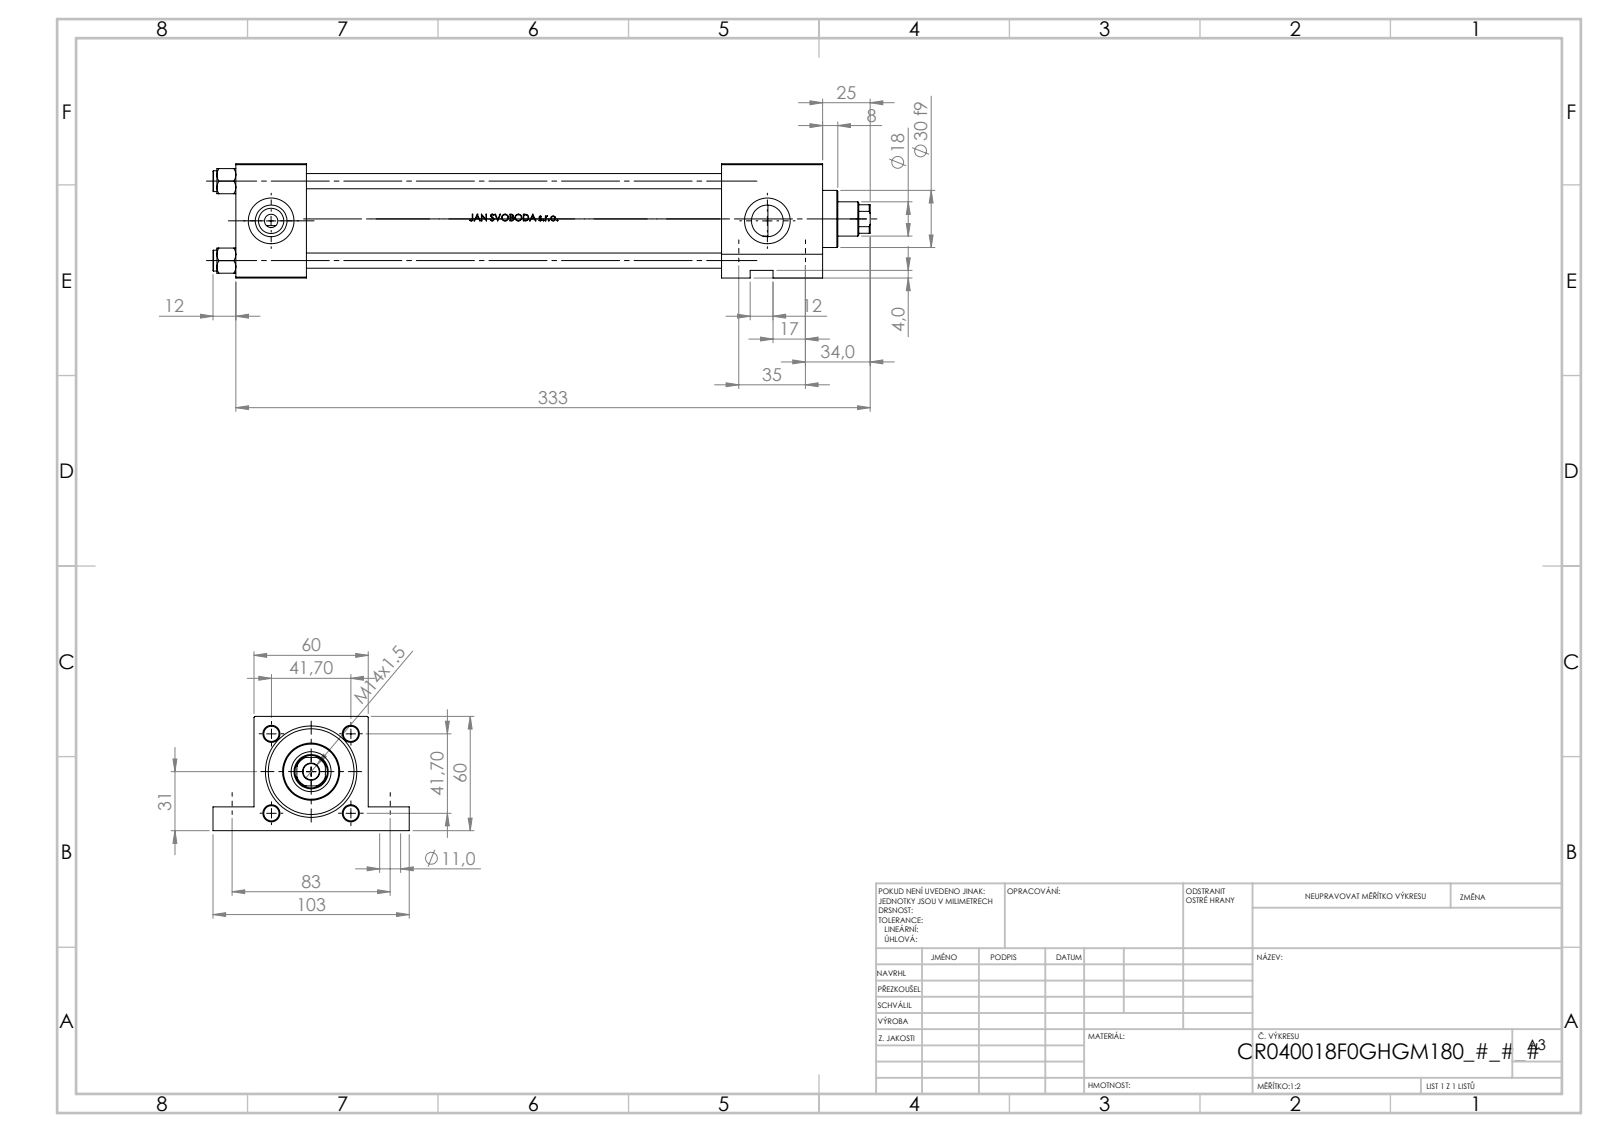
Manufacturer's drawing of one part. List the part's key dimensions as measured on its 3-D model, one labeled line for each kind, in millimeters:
Part name (STEP PRODUCT): V215_VC_A; V215CR_VCP_F; V215CR_F_TYCINKA; V215CR_F_Body (+1 more)
STEP written by: SolidWorks 2019 (CONFIG_CONTROL_DESIGN)
Units: millimetres
Bodies: 11 solids, 1118 faces (437 planar, 141 cylindrical, 540 other)
Overall size (bounding box): 345 × 103 × 60
Volume: 561 359 mm³ · Surface area: 179 898 mm²
Round holes (diameter × count): ⌀8 ×4, ⌀11 ×4, ⌀7 ×2, ⌀16.66 ×2, ⌀24 ×2, ⌀8.5 ×1, ⌀18 ×1, ⌀21 ×1, ⌀31 ×1, ⌀40 ×1, ⌀45 ×1
Round bosses / shafts (diameter × count): ⌀11 ×4, ⌀46 ×1, ⌀30 ×1
Partial cylindrical surfaces — rounded edges, fillets, slot ends (radius × count): R8.5 ×1
Main face-to-face distances: 60, 37, 308, 271, 255, 218, 53, 279.3, 242.3, 24.3
Hole centre spacings: 41.7, 28.79, 30.2, 35, 58.97, 83, 90.08, 260.5
